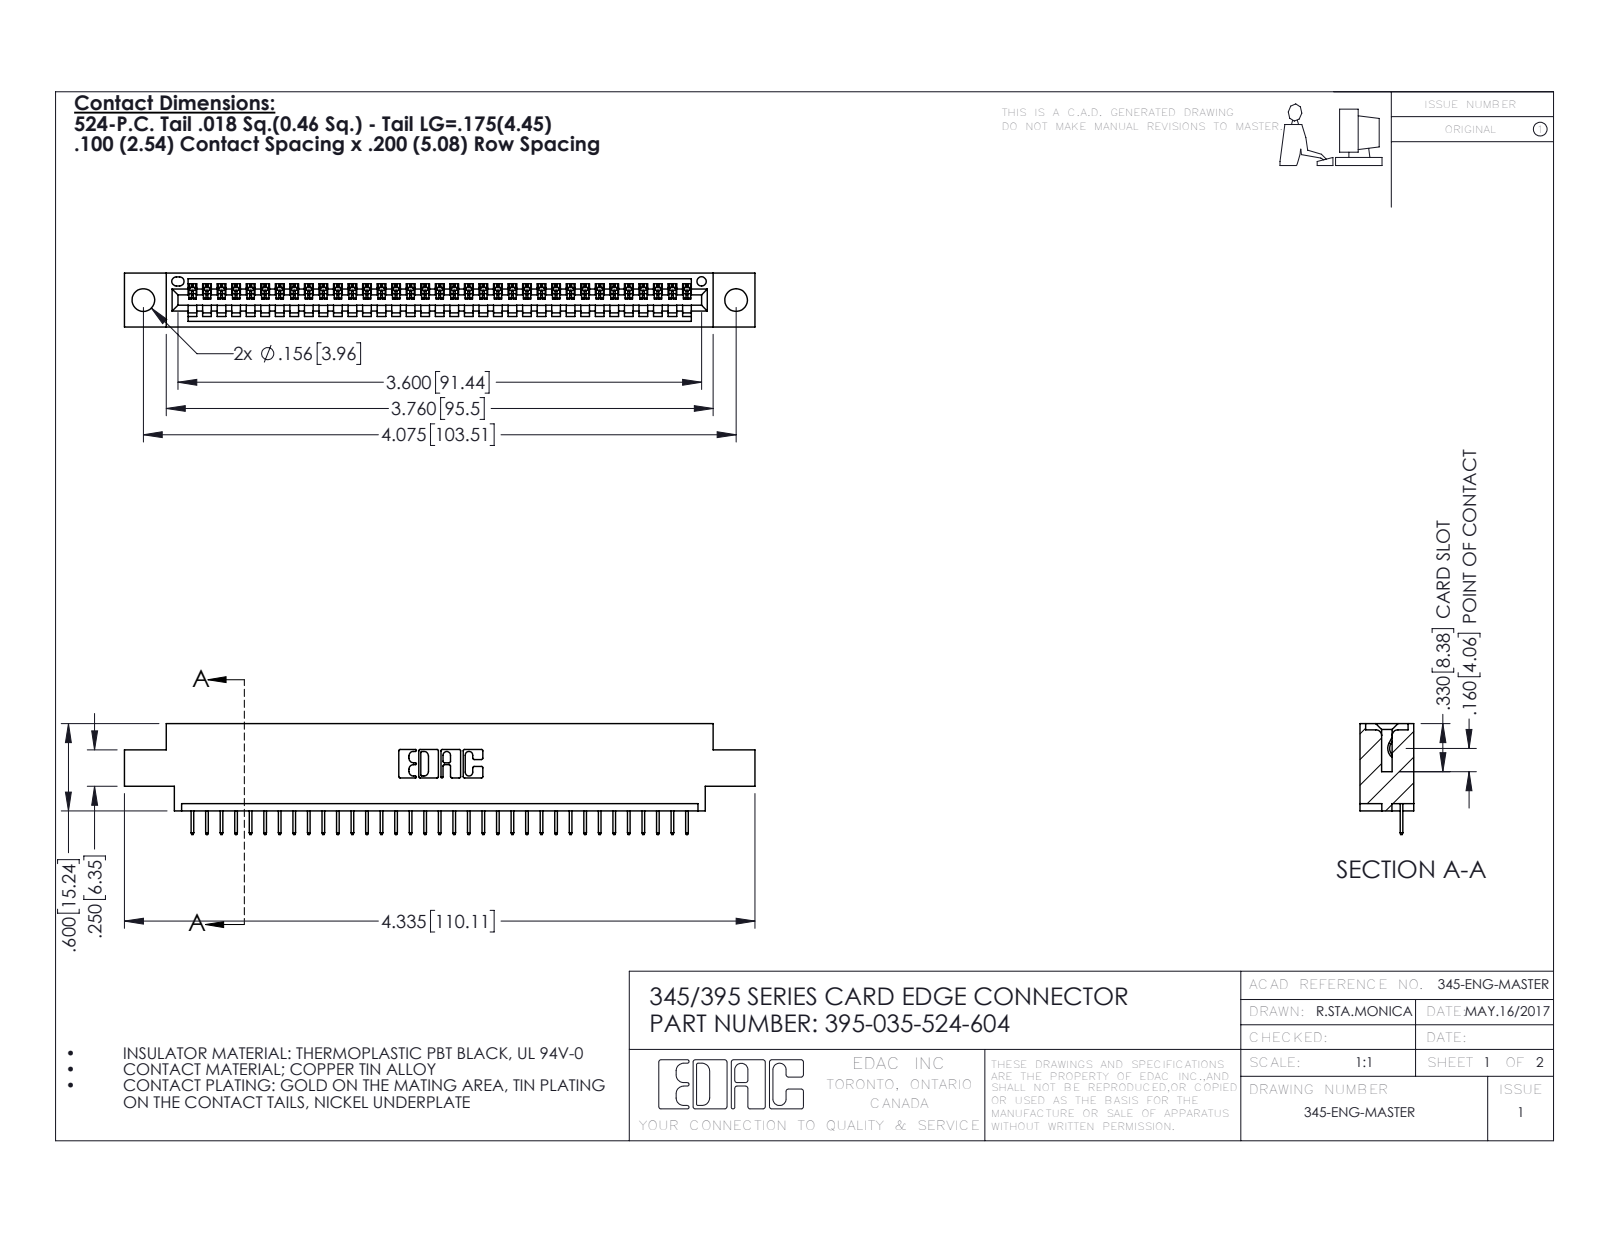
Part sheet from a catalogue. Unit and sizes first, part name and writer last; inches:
Units: inches
Overall size (bounding box): 4.335 × 0.762 × 0.37
Round holes (diameter × count): ⌀0.156 ×2, ⌀0.064 ×1
Partial cylindrical surfaces — rounded edges, fillets, slot ends (radius × count): R0.006 ×70, R0.01 ×22, R0.007 ×6, R0.031 ×6, R0.026 ×3, R0.031 ×2, R0.04 ×2, R0.014 ×1
Main face-to-face distances: 0.072, 0.298, 0.37, 0.2, 0.098, 0.272, 0.025, 0.225, 0.072, 0.175
Hole centre spacings: 0.27, 3.839, 4.075
Volume: 0.614 in³ · Surface area: 19.79 in²
Bodies: 36 solids, 2300 faces (1694 planar, 606 cylindrical, 0 other)
Part name (STEP PRODUCT): 345 Part_0.170 Offset - 0.156 Dia-TH; 345-292-001_345-293-124; 395-035-524-604
STEP written by: SolidWorks 2016 (CONFIG_CONTROL_DESIGN)
